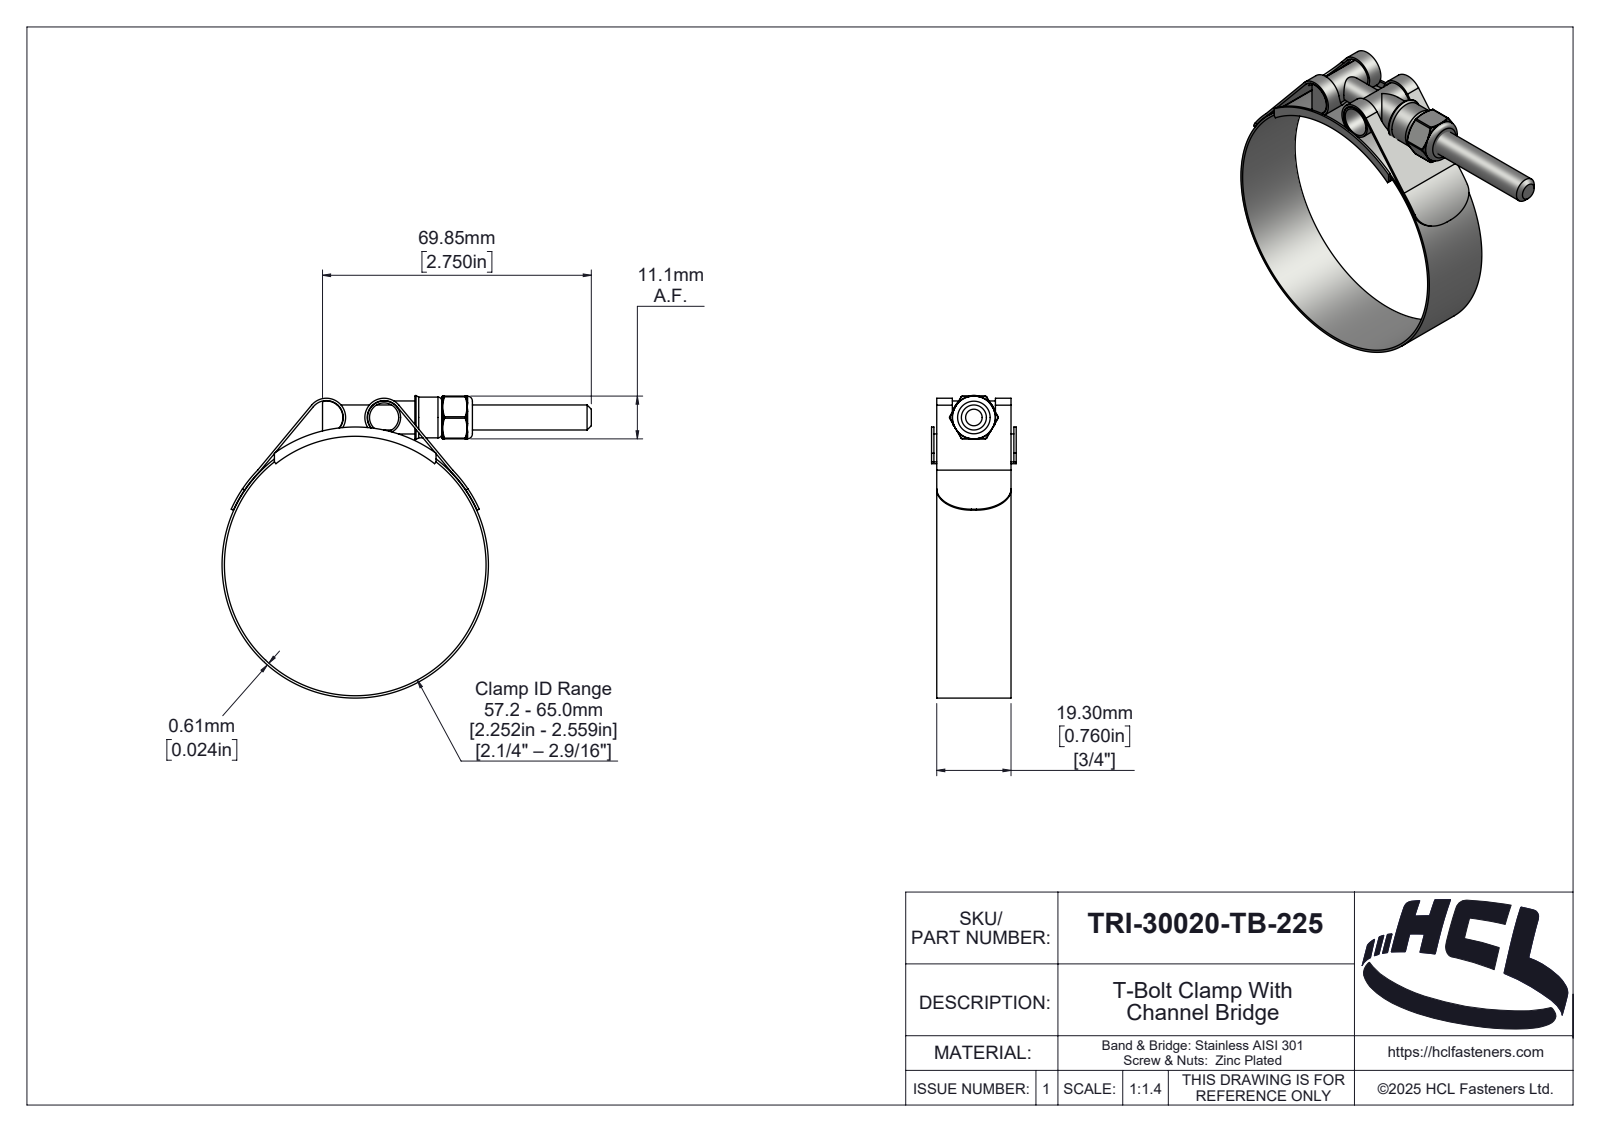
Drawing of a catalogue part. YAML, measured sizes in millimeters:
part_name: "TRI-30020-TB-225"
step_written_by: "SolidWorks 2025 (AUTOMOTIVE_DESIGN)"
units: millimeters
bodies: {solids: 6, faces: 330, planar: 44, cylindrical: 122, other: 164}
overall_size: [95.96, 78.6, 22]
volume: 8134
surface_area: 17834
round_holes:
  - {diameter: 5.4, count: 1}
  - {diameter: 6.35, count: 1}
  - {diameter: 6.5, count: 1}
  - {diameter: 7.58, count: 1}
  - {diameter: 68, count: 1}
round_bosses_or_shafts:
  - {diameter: 8.58, count: 2}
  - {diameter: 69.22, count: 1}
  - {diameter: 10.58, count: 1}
partial_cylinders:
  - {radius: 0.39, count: 6}
  - {radius: 0.5, count: 2}
  - {radius: 4.39, count: 2}
  - {radius: 5, count: 2}
  - {radius: 0.59, count: 1}
  - {radius: 2.42, count: 1}
  - {radius: 3.03, count: 1}
  - {radius: 3.19, count: 1}
face_to_face_distances: [0.61, 19.3, 0.74, 20.65, 1.35, 21.39, 20.04, 22, 11.11, 20.78]
hole_center_spacings: [39]
